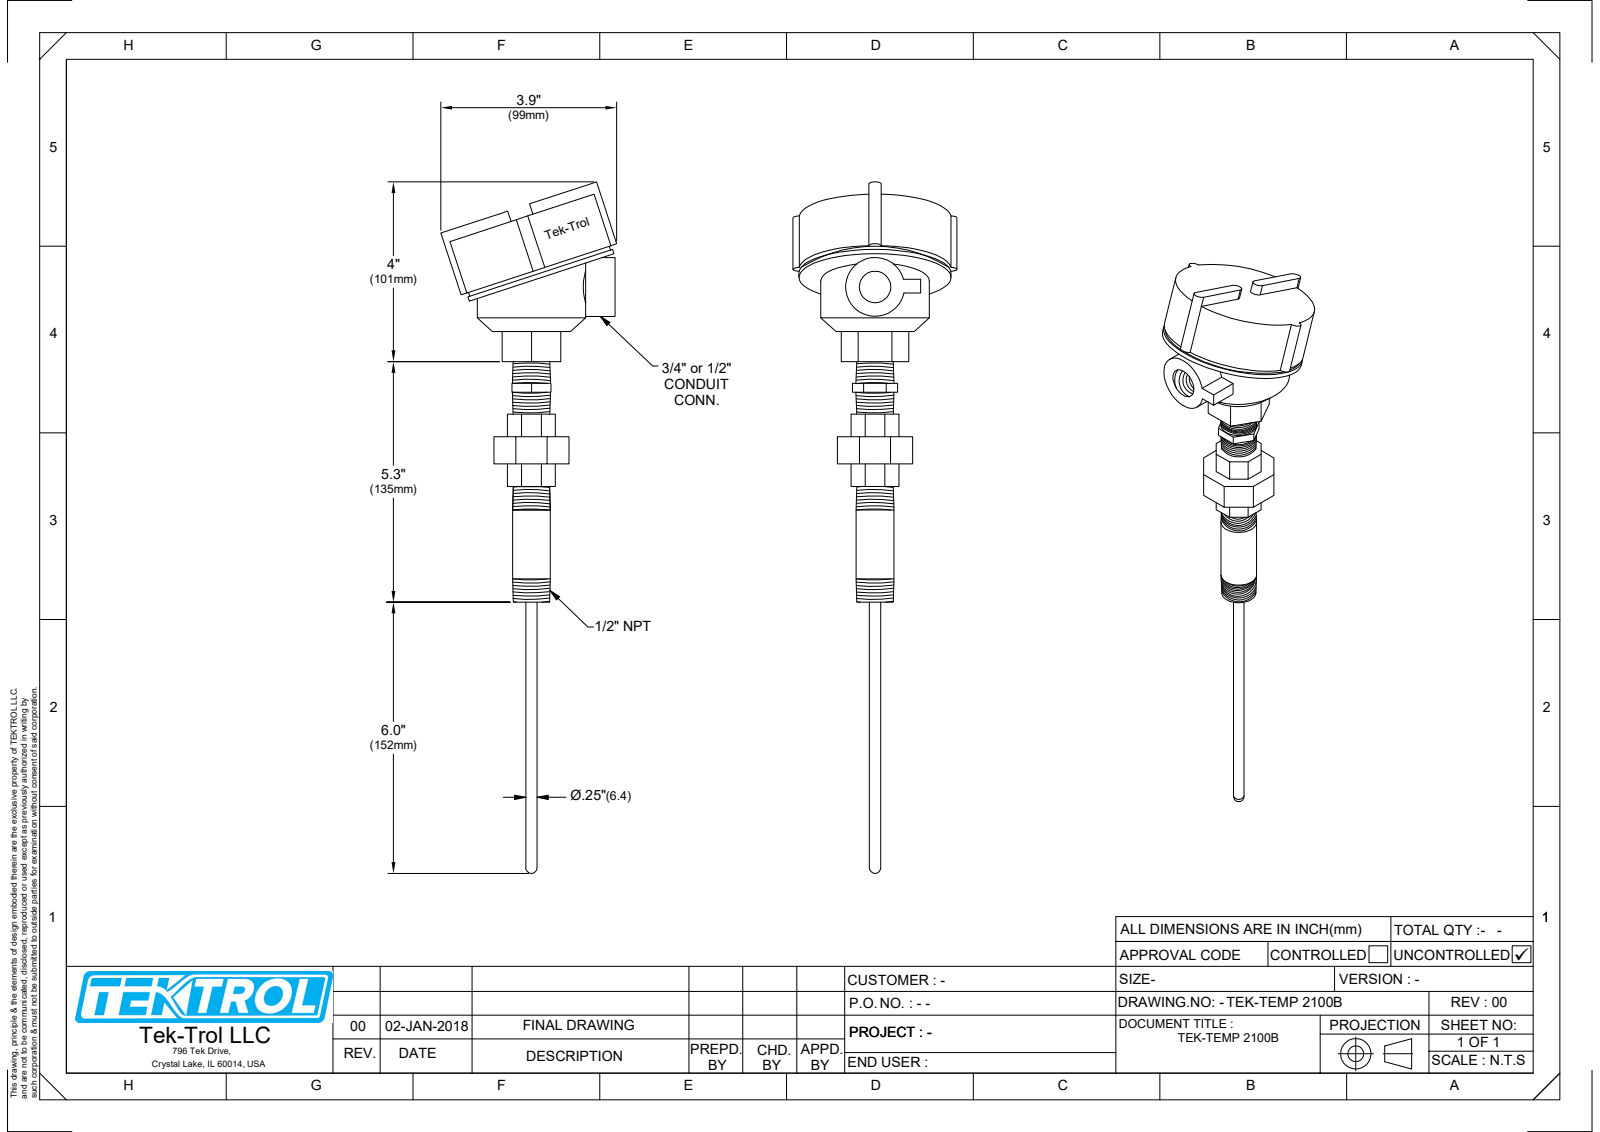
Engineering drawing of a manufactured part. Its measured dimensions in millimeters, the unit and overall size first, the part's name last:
Units: millimetres
Overall size (bounding box): 388.69 × 99.01 × 92.2
Round holes (diameter × count): ⌀17.78 ×2, ⌀16.1 ×1
Round bosses / shafts (diameter × count): ⌀85.6 ×1, ⌀85.56 ×1, ⌀83.31 ×1, ⌀60.96 ×1, ⌀33.02 ×1, ⌀21.27 ×1, ⌀6.35 ×1
Partial cylindrical surfaces — rounded edges, fillets, slot ends (radius × count): R3.43 ×6
Main face-to-face distances: 35.3, 7.66, 34.58, 16.89, 26.92, 32.9, 12.7, 27.94, 15.24, 42.24
Volume: 361 443 mm³ · Surface area: 57 978 mm²
Bodies: 2 solids, 94 faces (65 planar, 21 cylindrical, 8 other)
Part name (STEP PRODUCT): Explosion-Proof-Head-Nipple-Union-Nipple
STEP written by: Autodesk Inventor 2026 (AP242_MANAGED_MODEL_BASED_3D_ENGINEERING_MIM_LF)
